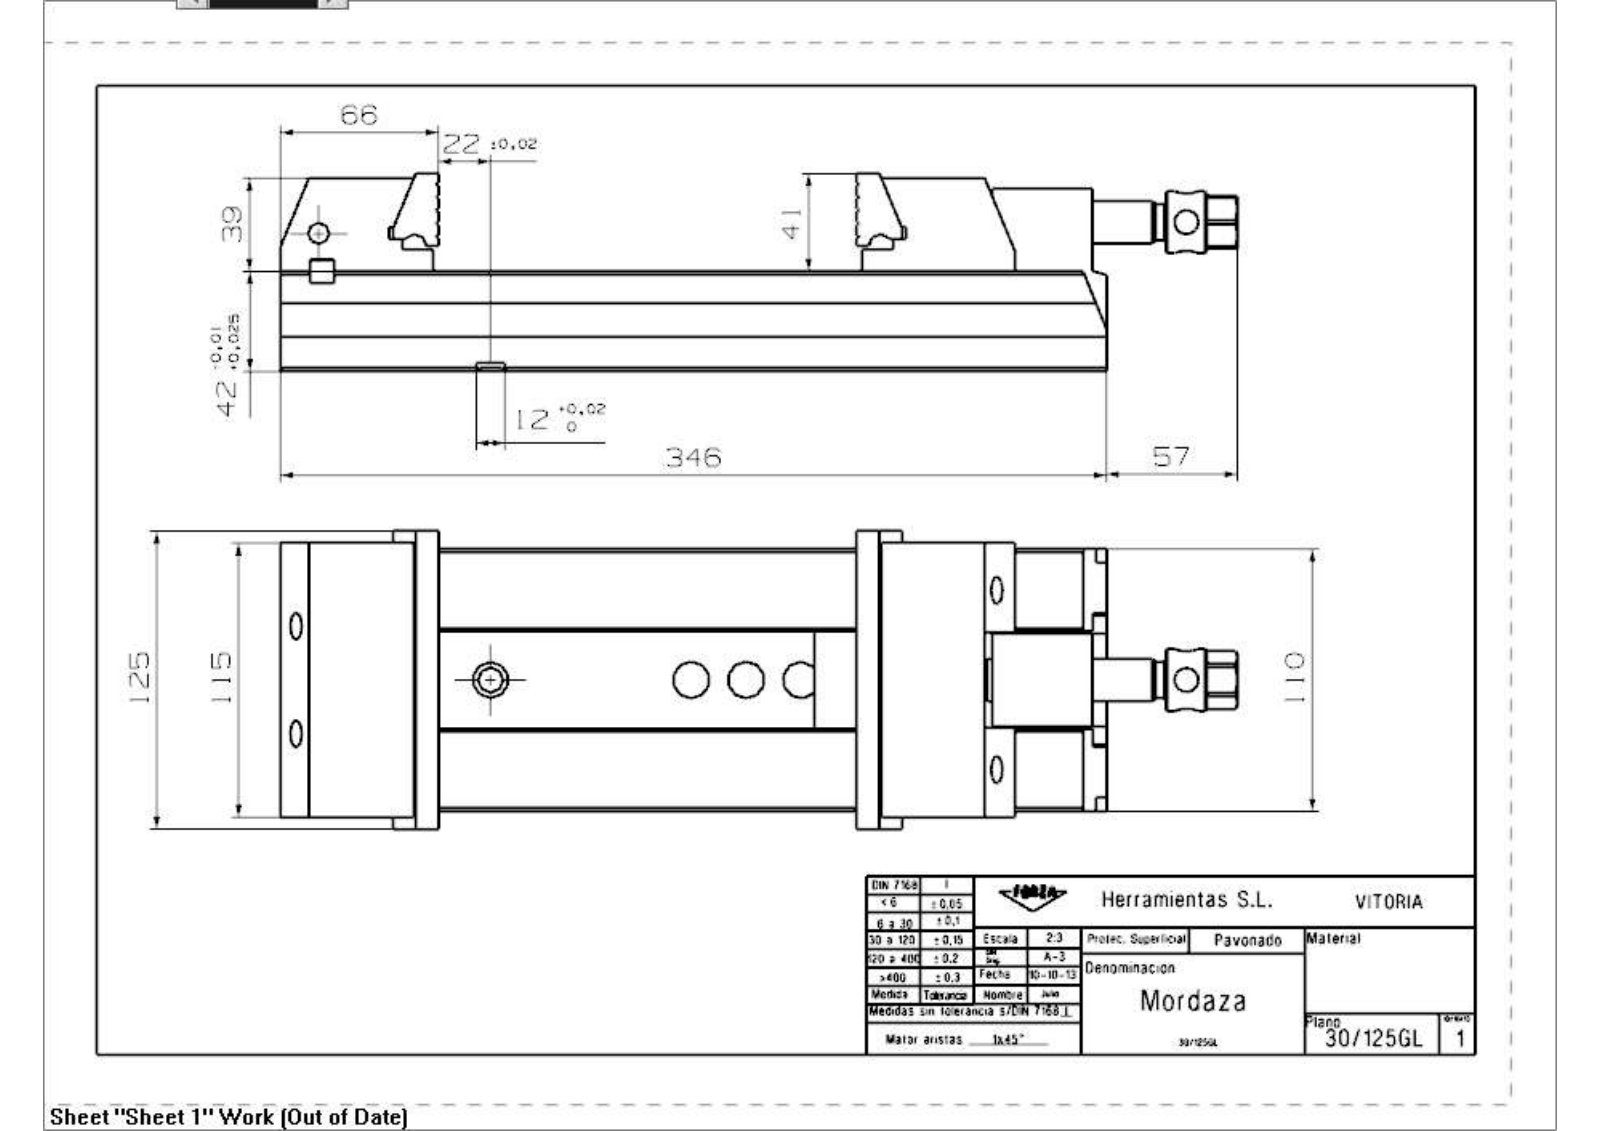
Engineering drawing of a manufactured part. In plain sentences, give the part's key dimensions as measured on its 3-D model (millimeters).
The part is named "PRD_125GL_Mordaza". Its 3-D file was written by "SIEMENS PLM Software NX 9.0 (CONFIG_CONTROL_DESIGN)". It is 11 solids with 458 faces: 290 planar, 122 cylindrical and 46 other. Overall it measures 400.83 by 125 by 83 millimeters. Its volume is 1 706 000 cubic millimeters and its surface area 291 946 square millimeters. Round holes: 4 of diameter 4.35, 4 of diameter 5.19, 4 of diameter 6.5, 4 of diameter 7.5, 4 of diameter 11.5, 4 of diameter 15, 3 of diameter 8.78, 2 of diameter 6.99, 2 of diameter 8, 2 of diameter 10, 2 of diameter 10.5, 2 of diameter 11. Round bosses or shafts: 1 of diameter 26, 1 of diameter 17.73, 1 of diameter 15, 1 of diameter 14.5, 1 of diameter 10.5. Partial cylindrical surfaces (rounded edges, fillets, slot ends): 20 of radius 0.3, 7 of radius 6, 4 of radius 10, 4 of radius 16, 2 of radius 1.6, 2 of radius 5, 1 of radius 3, 1 of radius 8. The main face-to-face distances are 42, 15.4, 26.6, 6, 27, 8.5, 39, 77, 29.5, 13. The hole center spacings are 60, 75, 0.7, 8.95, 9.19, 15, 15.02, 23.16.
